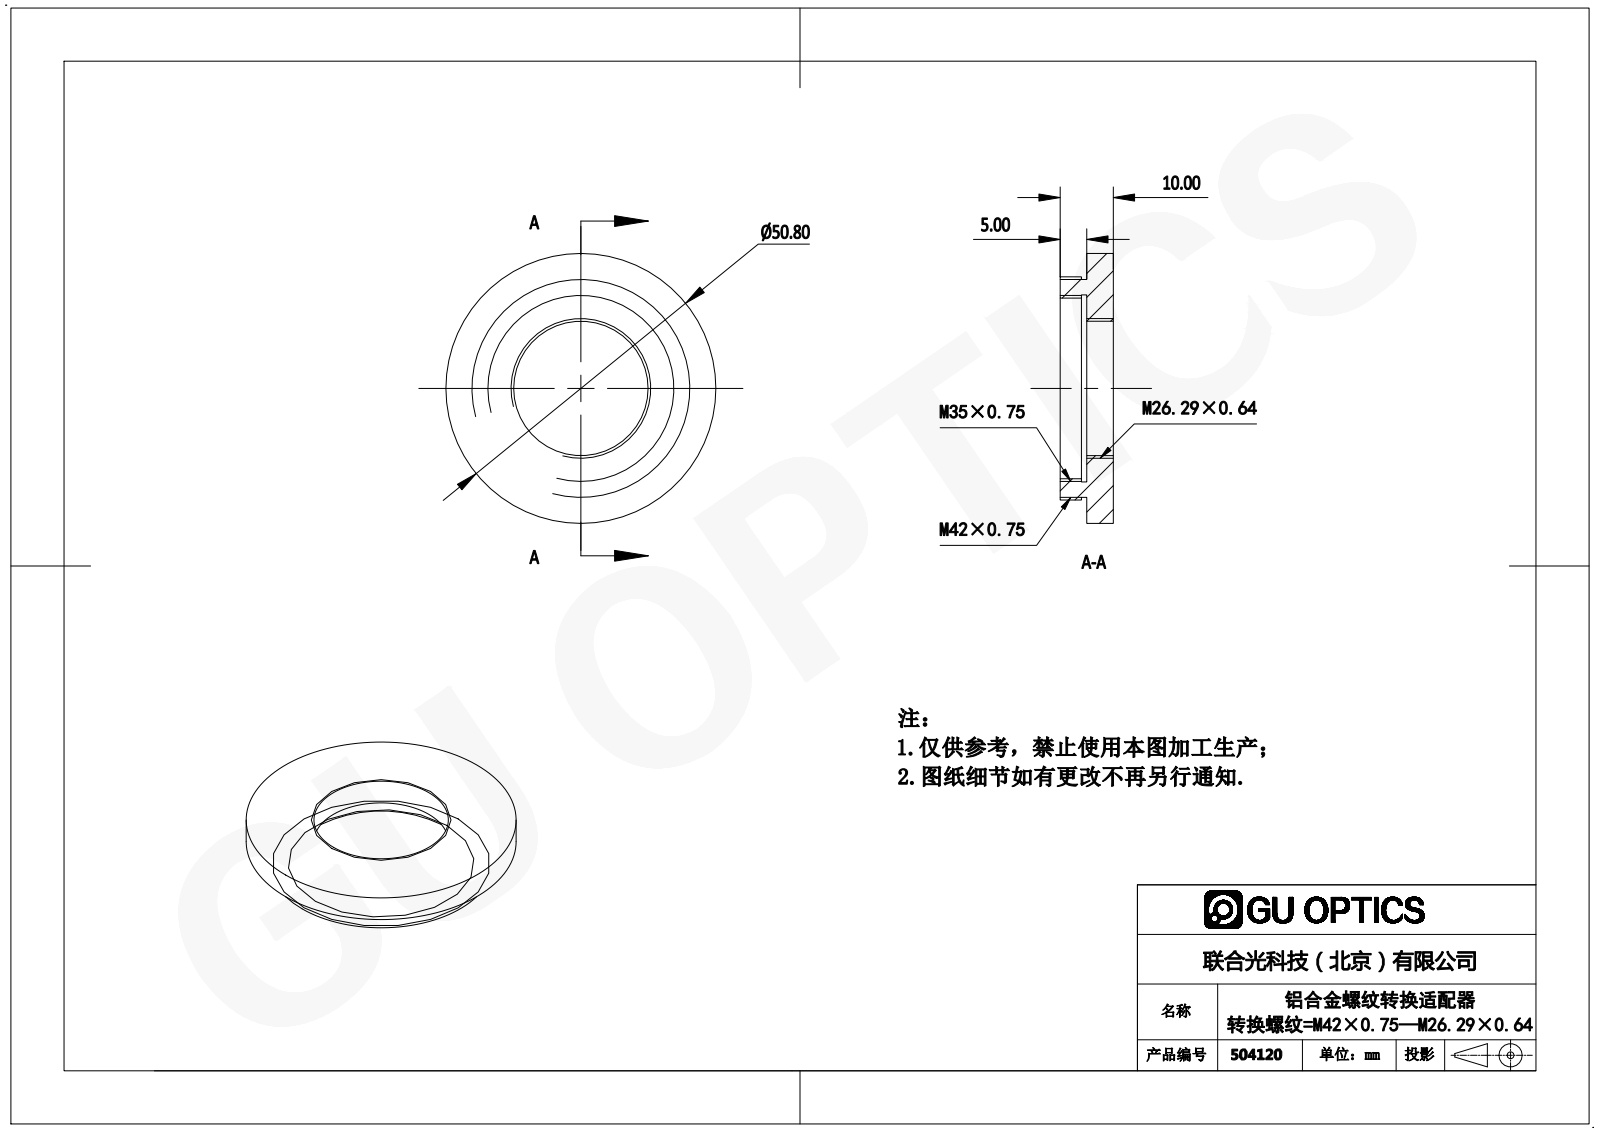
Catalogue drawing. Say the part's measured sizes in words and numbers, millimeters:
The part is named "504120". Its 3-D file was written by "SolidWorks 2016 (AUTOMOTIVE_DESIGN)". It is 1 solid with 18 faces: 6 planar, 12 cylindrical and 0 other. Overall it measures 50.8 by 50.8 by 10 millimeters. Its volume is 9 880 cubic millimeters and its surface area 5 699 square millimeters. Round holes: 1 of diameter 25.29, 1 of diameter 34, 1 of diameter 35.2. Round bosses or shafts: 1 of diameter 50.8, 1 of diameter 42, 1 of diameter 41. The main face-to-face distances are 5, 10, 4, 1, 6.
